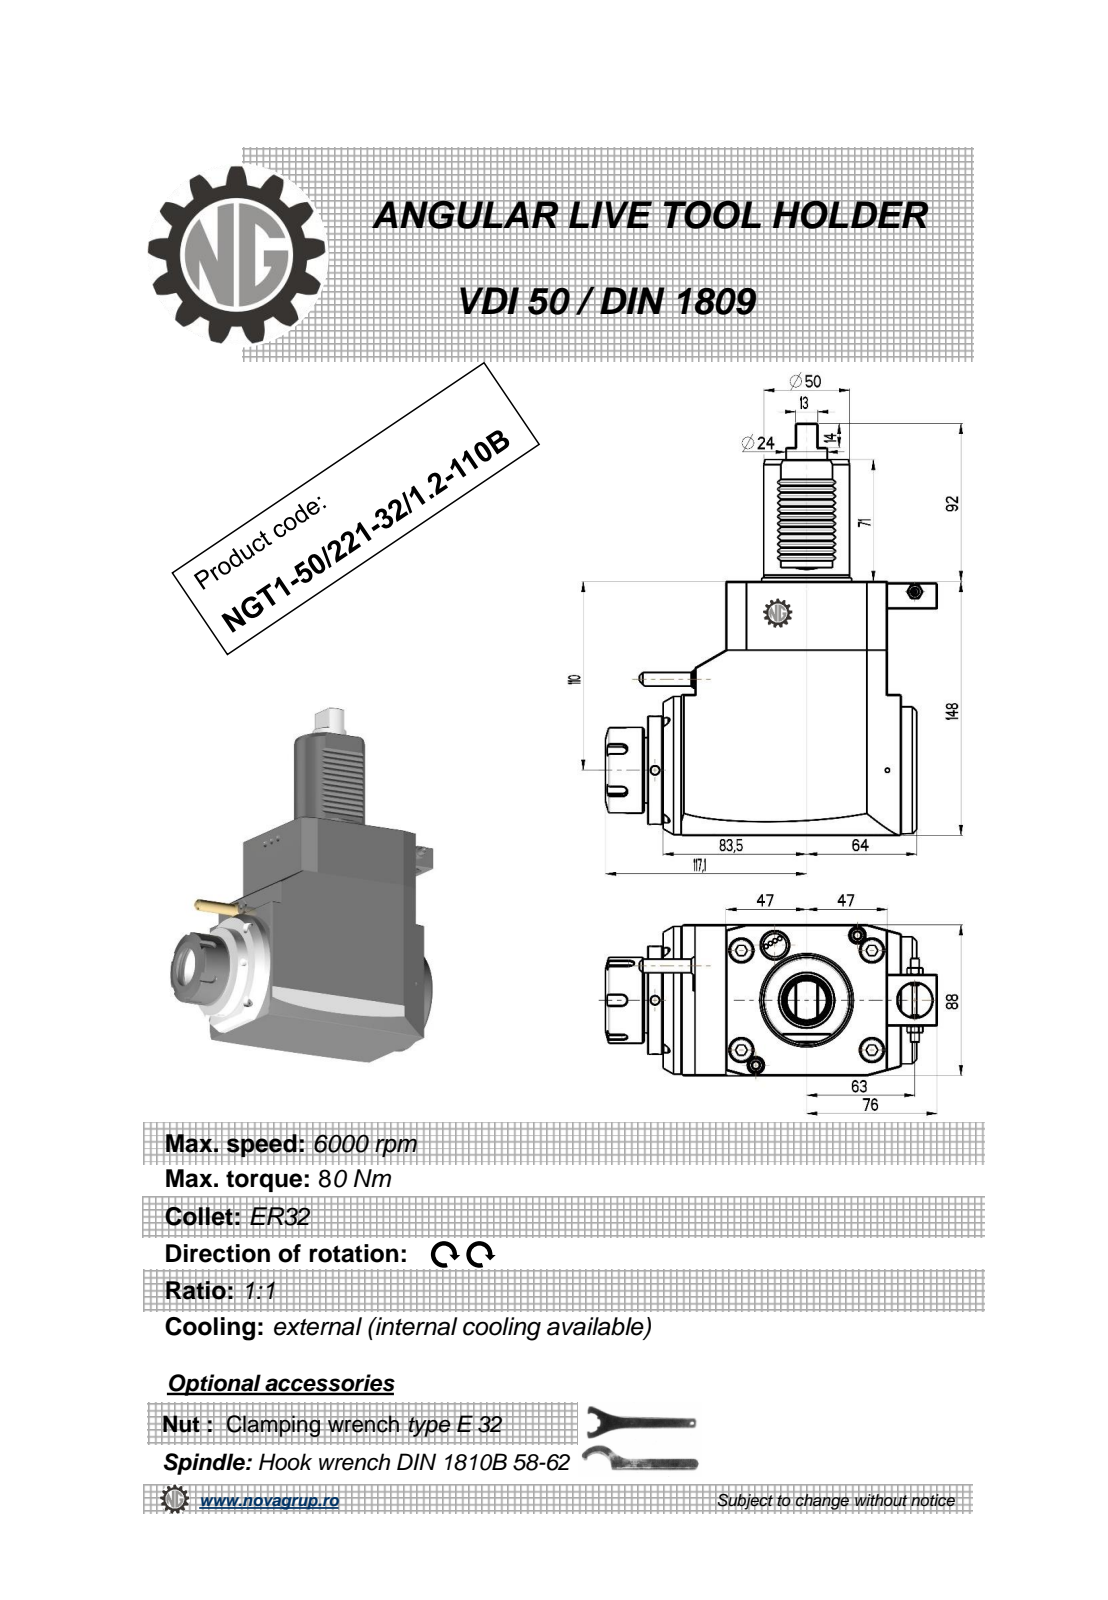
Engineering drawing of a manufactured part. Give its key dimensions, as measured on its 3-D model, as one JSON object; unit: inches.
{"part_name": "NGT1_50_221_32_1_2_110B", "step_written_by": "PRO/ENGINEER BY PARAMETRIC TECHNOLOGY CORPORATION, 2010280 (CONFIG_CONTROL_DESIGN)", "units": "inches", "bodies": {"solids": 1, "faces": 417, "planar": 198, "cylindrical": 95, "other": 124}, "overall_size": [9.449, 7.602, 3.465], "volume_in3": 109.7, "surface_area_in2": 172.8, "round_holes": [[0.197, 3], [0.15, 2], [0.157, 2], [0.118, 1], [0.374, 1], [0.787, 1], [1.063, 1]], "round_bosses_or_shafts": [[1.969, 2], [3.386, 1], [2.913, 1], [2.48, 1], [1.988, 1], [1.614, 1], [0.945, 1], [0.394, 1]], "partial_cylinders_radius": [[0.01, 12], [0.012, 12], [0.008, 6], [0.118, 5], [0.031, 2], [0.098, 1]], "face_to_face_distances": [3.465, 5.827, 5.807, 0.354, 0.669, 0.315, 3.701, 4.37, 1.437, 5.138], "hole_center_spacings": [0.354, 4.012, 0.709, 1.958, 2.065, 2.225, 2.23, 3.996]}
